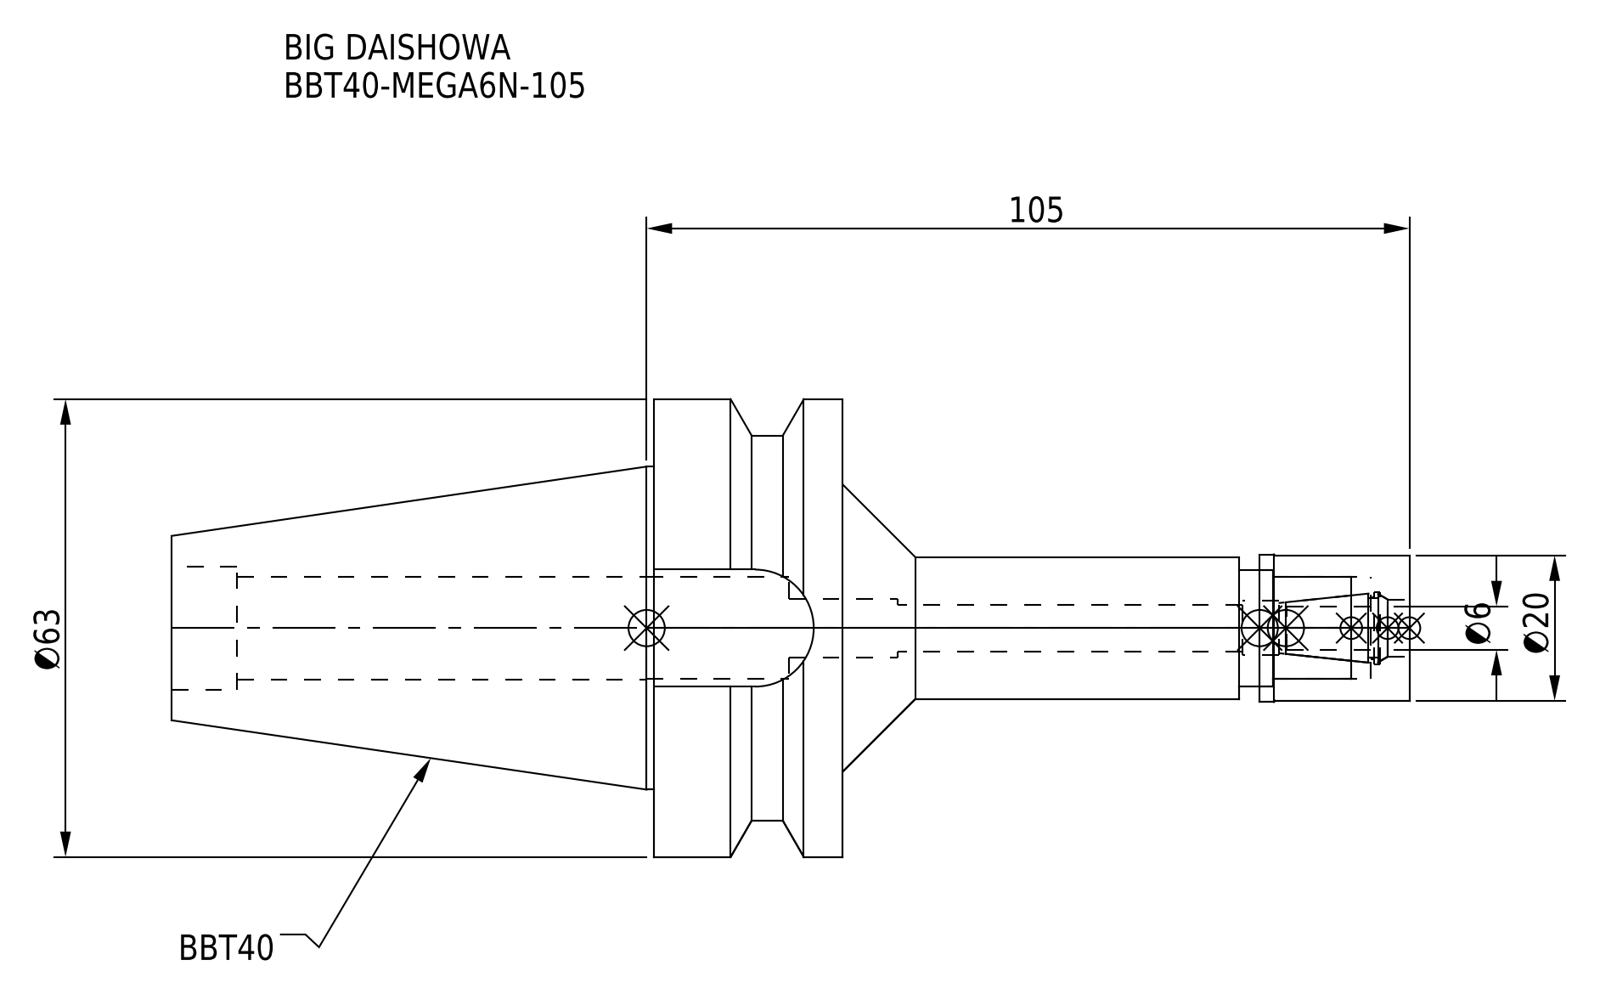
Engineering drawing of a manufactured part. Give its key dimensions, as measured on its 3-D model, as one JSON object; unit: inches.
{"part_name": "BBT40MN06105-060_ASM.stp; BBT40-MEGA6N-105_1.stp; MGN6_1.stp; DXF_TEMP_ASSY_ASM_4_ASM.stp (+3 more)", "step_written_by": "SolidWorks 2019 (CONFIG_CONTROL_DESIGN)", "units": "inches", "bodies": {"solids": 2, "faces": 80, "planar": 24, "cylindrical": 42, "other": 14}, "overall_size": [6.709, 2.48, 2.48], "volume_in3": 8.87, "surface_area_in2": 47.76, "round_holes": [[0.252, 1], [0.295, 1], [0.311, 1], [0.315, 1], [0.335, 1], [0.394, 1], [0.551, 1], [0.559, 1], [0.63, 1], [0.669, 1]], "round_bosses_or_shafts": [[2.48, 1], [2.087, 1], [1.75, 1], [0.799, 1], [0.787, 1], [0.768, 1]], "partial_cylinders_radius": [[0.317, 1]], "face_to_face_distances": [1.024, 1.772, 2.614, 3.638, 3.071, 4.094, 6.709, 0.634, 2.26, 3.283]}
